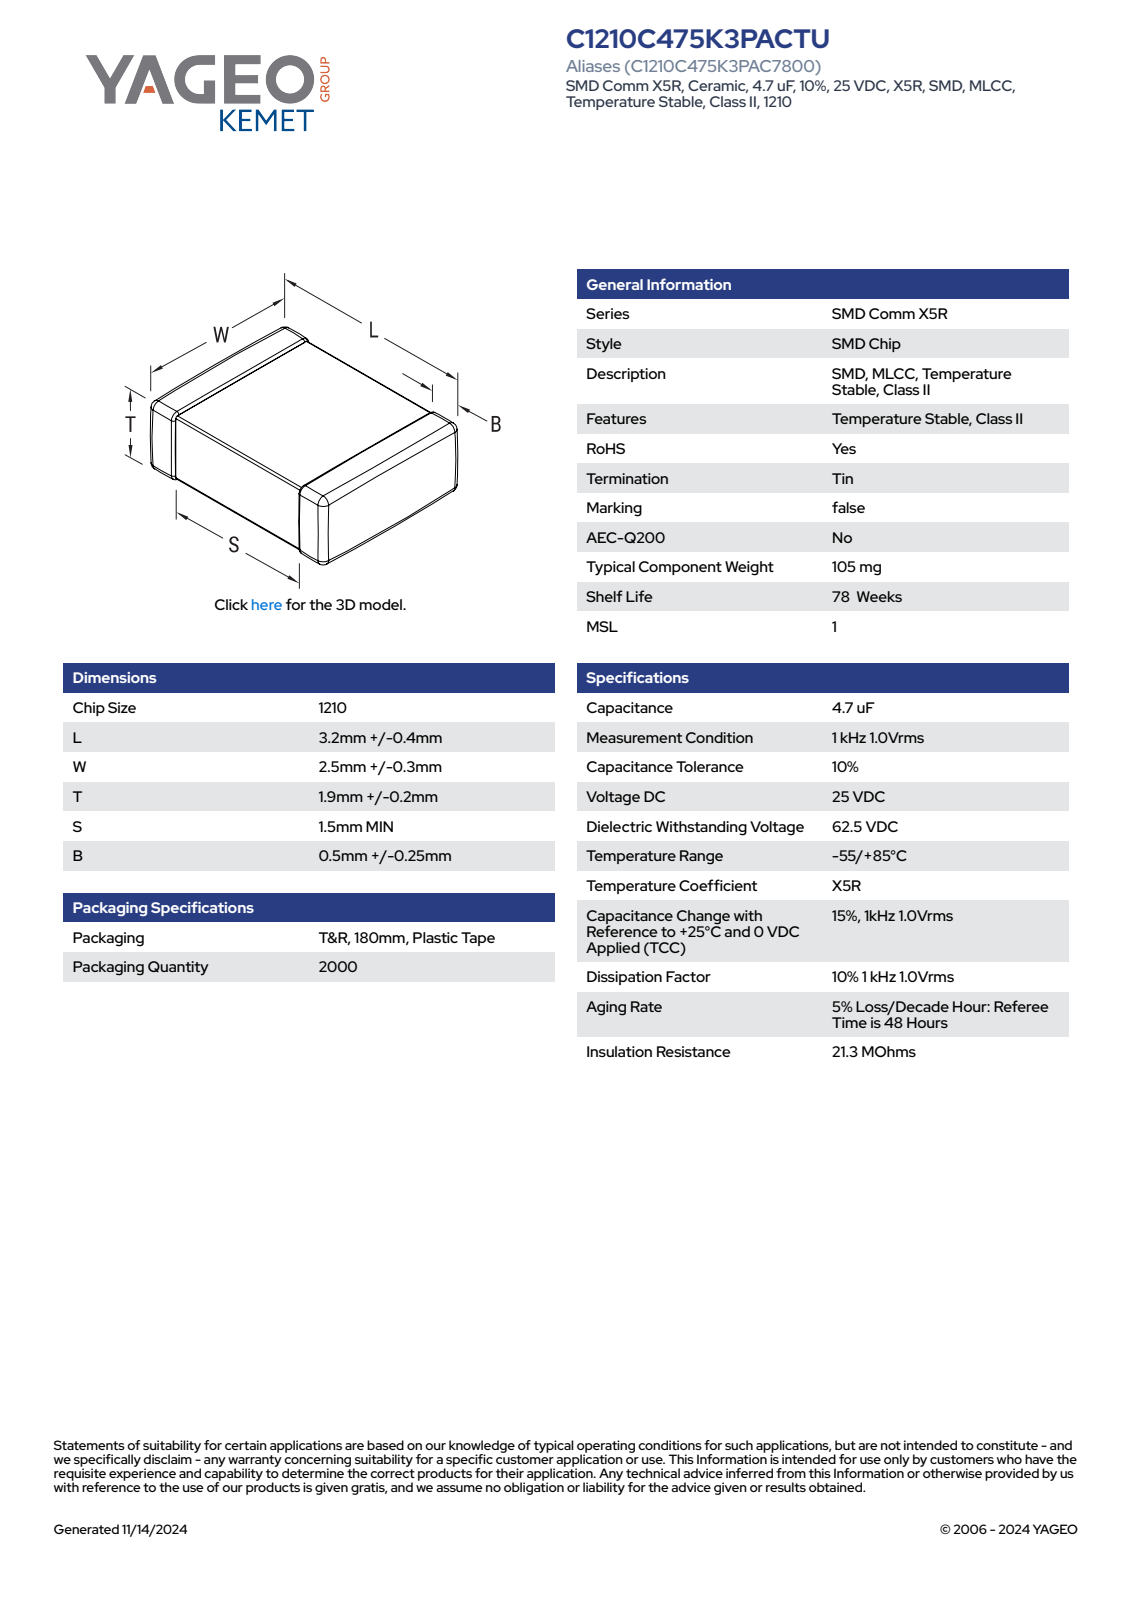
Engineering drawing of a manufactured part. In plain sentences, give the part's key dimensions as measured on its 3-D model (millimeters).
The part is named "CCS_CCSTDNOS_1210_L3.6W2.8T2.1B0.75". Its 3-D file was written by "SolidWorks 2021 (AUTOMOTIVE_DESIGN)". It is 4 solids with 125 faces: 71 planar, 38 cylindrical and 16 other. Overall it measures 3.6 by 2.8 by 2.1 millimeters. Its volume is 20 cubic millimeters and its surface area 46 square millimeters. The main face-to-face distances are 2.04, 1.98, 3.6, 2.74, 2.68, 2.1, 2.8, 2.05, 1.99, 1.35.
